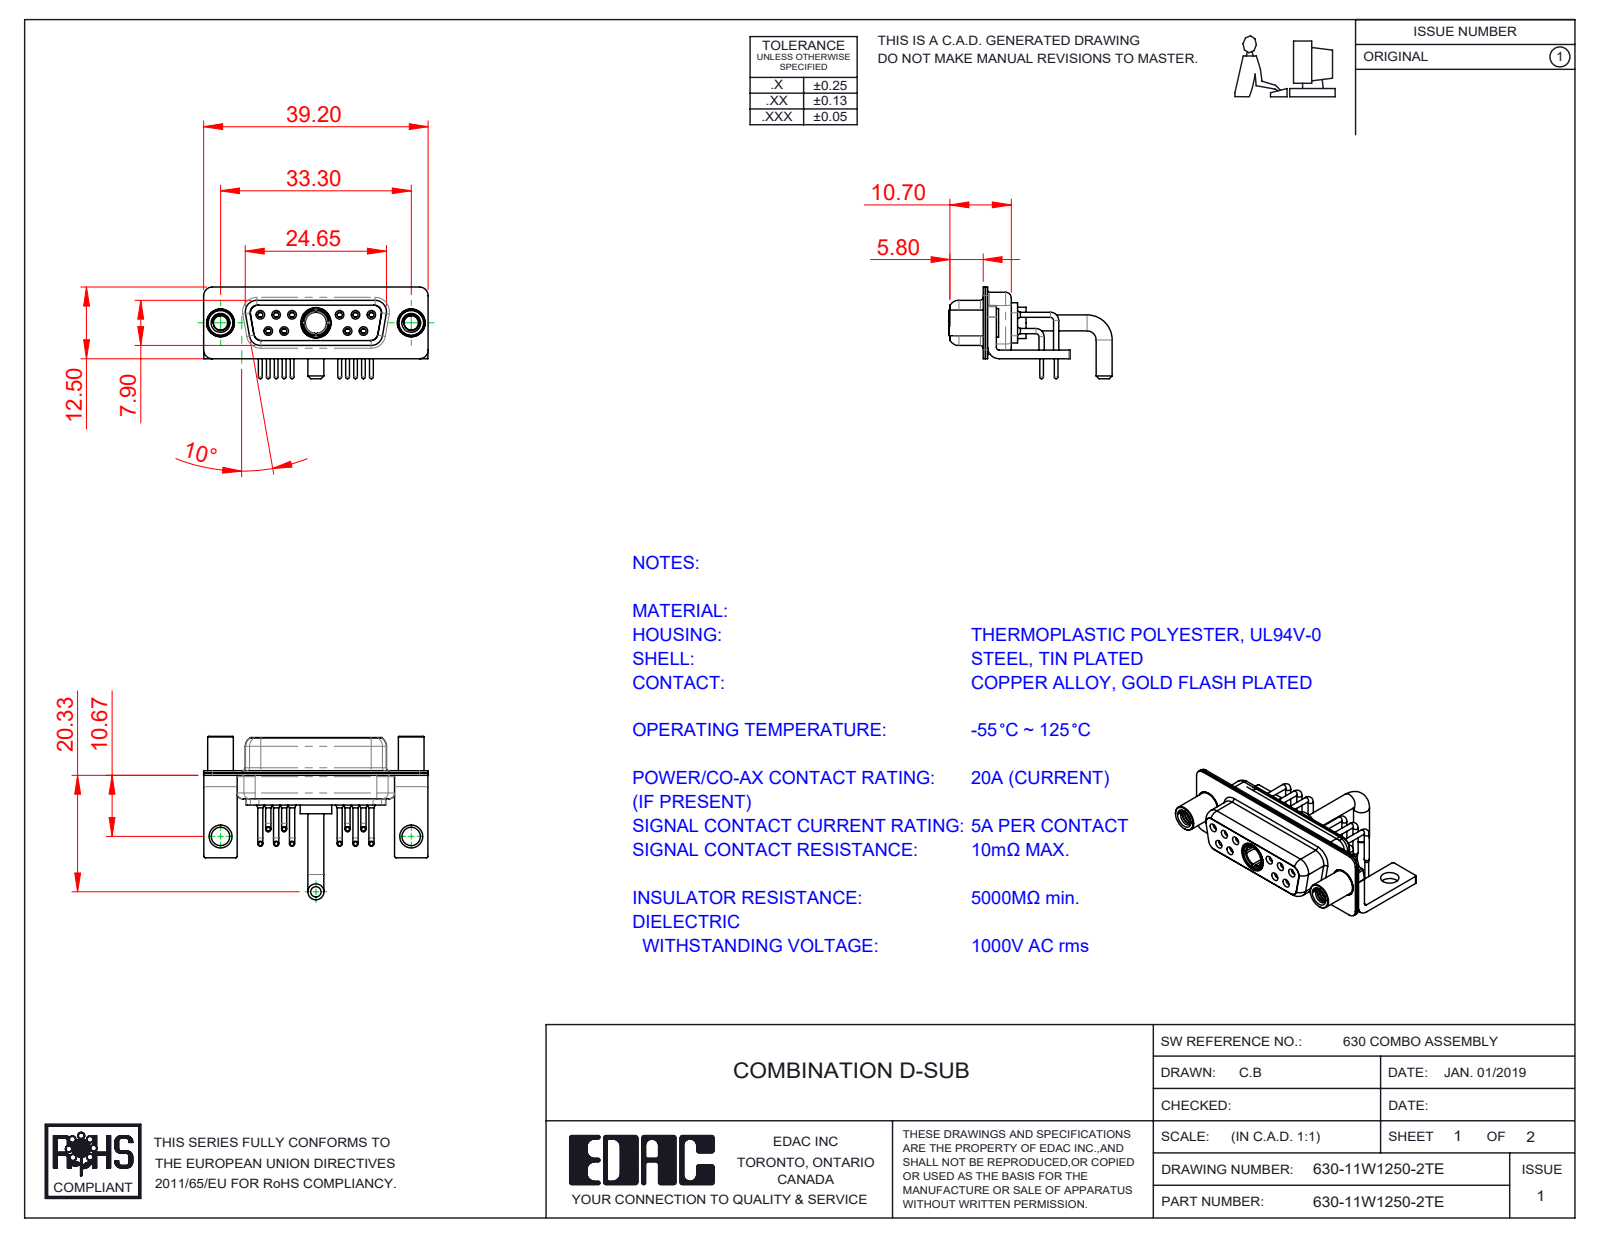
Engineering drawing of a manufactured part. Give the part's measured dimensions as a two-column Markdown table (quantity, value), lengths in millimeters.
| quantity | value |
| --- | --- |
| part name | 630Combo Stabilizer Bracket; 630-11W1250-2TE; 630Combo Threaded Standoff_D; 630Combo Housing_11W1 (+5 more) |
| STEP written by | SolidWorks 2020 (CONFIG_CONTROL_DESIGN) |
| units | millimeters |
| bodies | 19 solids, 985 faces (268 planar, 464 cylindrical, 253 other) |
| overall size | 39.2 × 28.53 × 16 |
| volume | 3 074 mm³ |
| surface area | 7 259 mm² |
| round holes (diameter × count) | 0.9 × 10, 1.1 × 10, 1.5 × 10, 2 × 10, 1.7 × 6, 1.6 × 4, 4.85 × 3, 2.5 × 2, 3.2 × 2, 4 × 2, 4.05 × 2, 3.7 × 1 |
| round bosses / shafts (diameter × count) | 0.9 × 10, 0.65 × 10, 1.6 × 6, 5 × 2, 4.95 × 2, 4.8 × 2, 4.5 × 2, 2.8 × 2 |
| partial cylindrical surfaces (radius × count) | 0.25 × 16, 1.5 × 16, 2 × 13, 1.35 × 12, 1.6 × 8, 0.5 × 5, 0.6 × 4, 0.65 × 4 |
| main face-to-face distances | 0.4, 0.8, 1.4, 0.45, 8.45, 1.5, 1.8, 8.9, 6.2, 2.3 |
| hole center spacings | 3.16, 2.77, 13.85, 11.08, 16.62, 5.03, 5.04, 5.54 |
